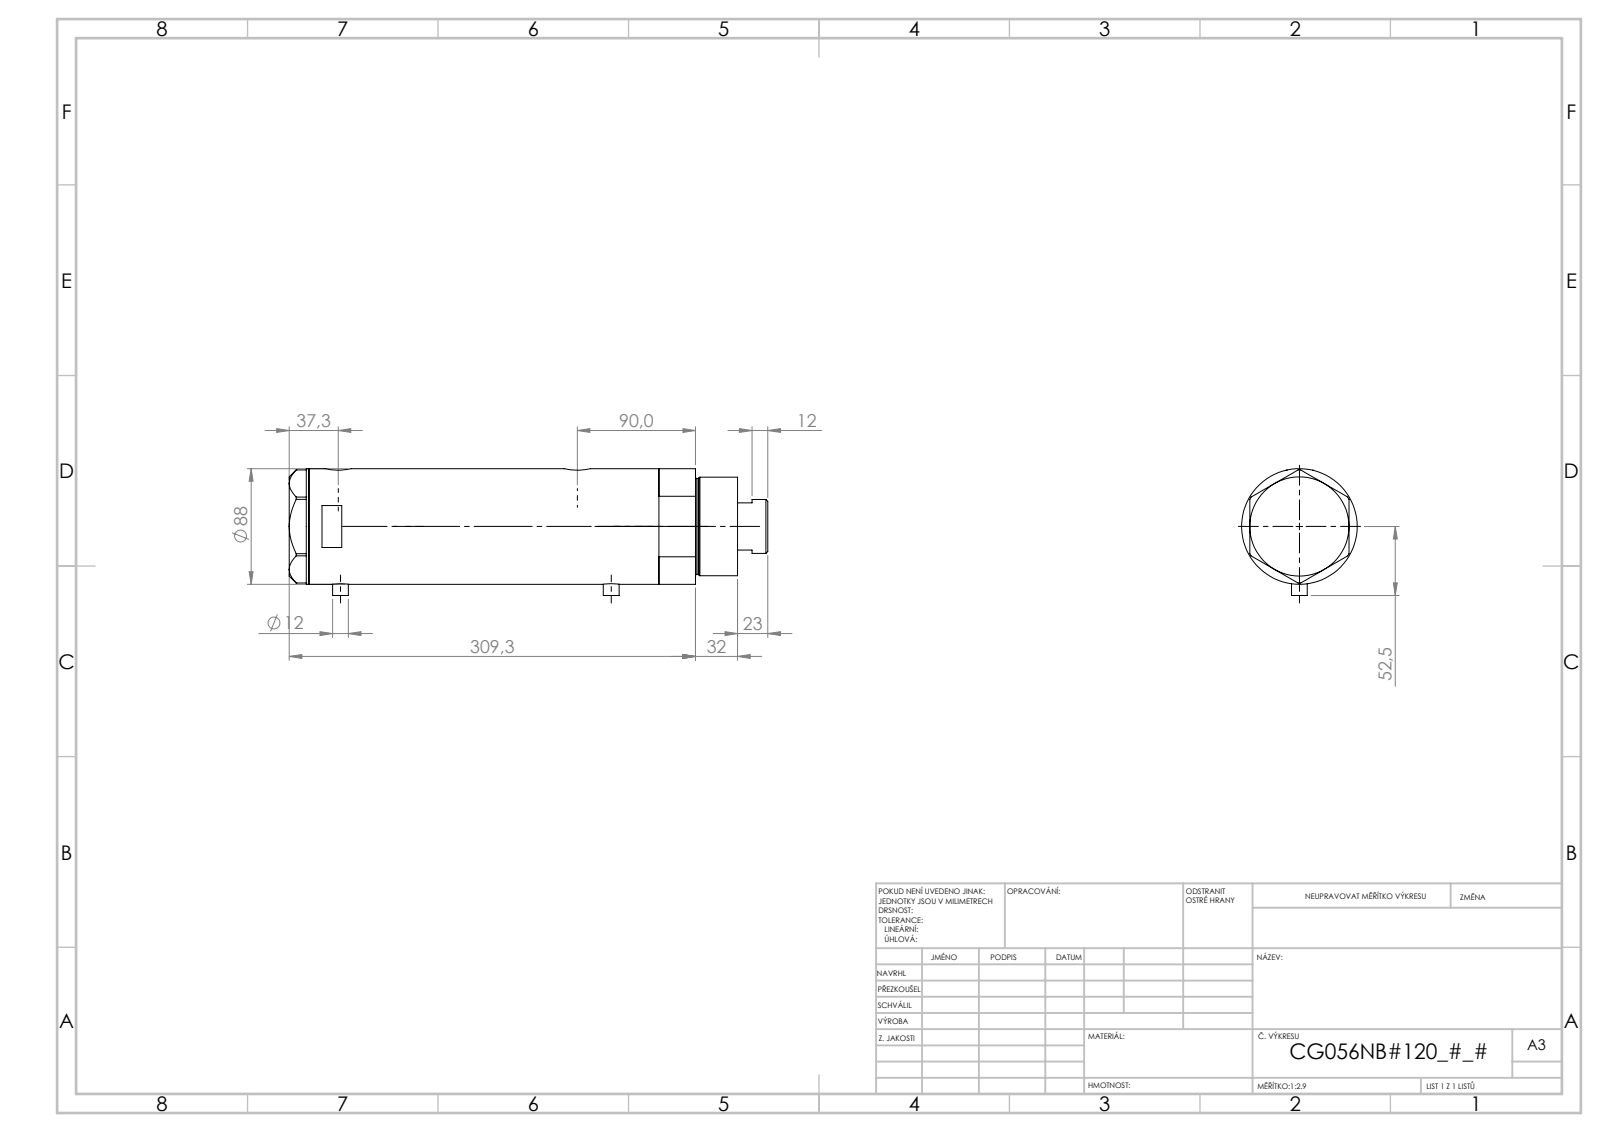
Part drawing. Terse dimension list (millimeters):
name: V270CG_FRONT; V270CG_VC; V270CG_MIDDLE; V270CG_BACK
written by: SolidWorks 2019 (CONFIG_CONTROL_DESIGN)
unit: mm
bodies: 4 solids, 126 faces (53 planar, 53 cylindrical, 20 other)
size: 344.47 × 89.1 × 88
volume: 1 762 000 mm³; area: 250 380 mm²
holes: 2× ⌀5, 2× ⌀12.5, 2× ⌀13.16, 2× ⌀20, 1× ⌀14.5, 1× ⌀42, 1× ⌀43.5, 1× ⌀56, 1× ⌀60, 1× ⌀80
bosses: 2× ⌀12, 1× ⌀88, 1× ⌀75, 1× ⌀73, 1× ⌀41
face distances: 194.4, 26, 168.4, 15, 41, 209.4, 306.47, 321.47, 280.47, 112.07
hole spacings: 1.7, 25.8, 170.3, 172, 196.1, 197.8
